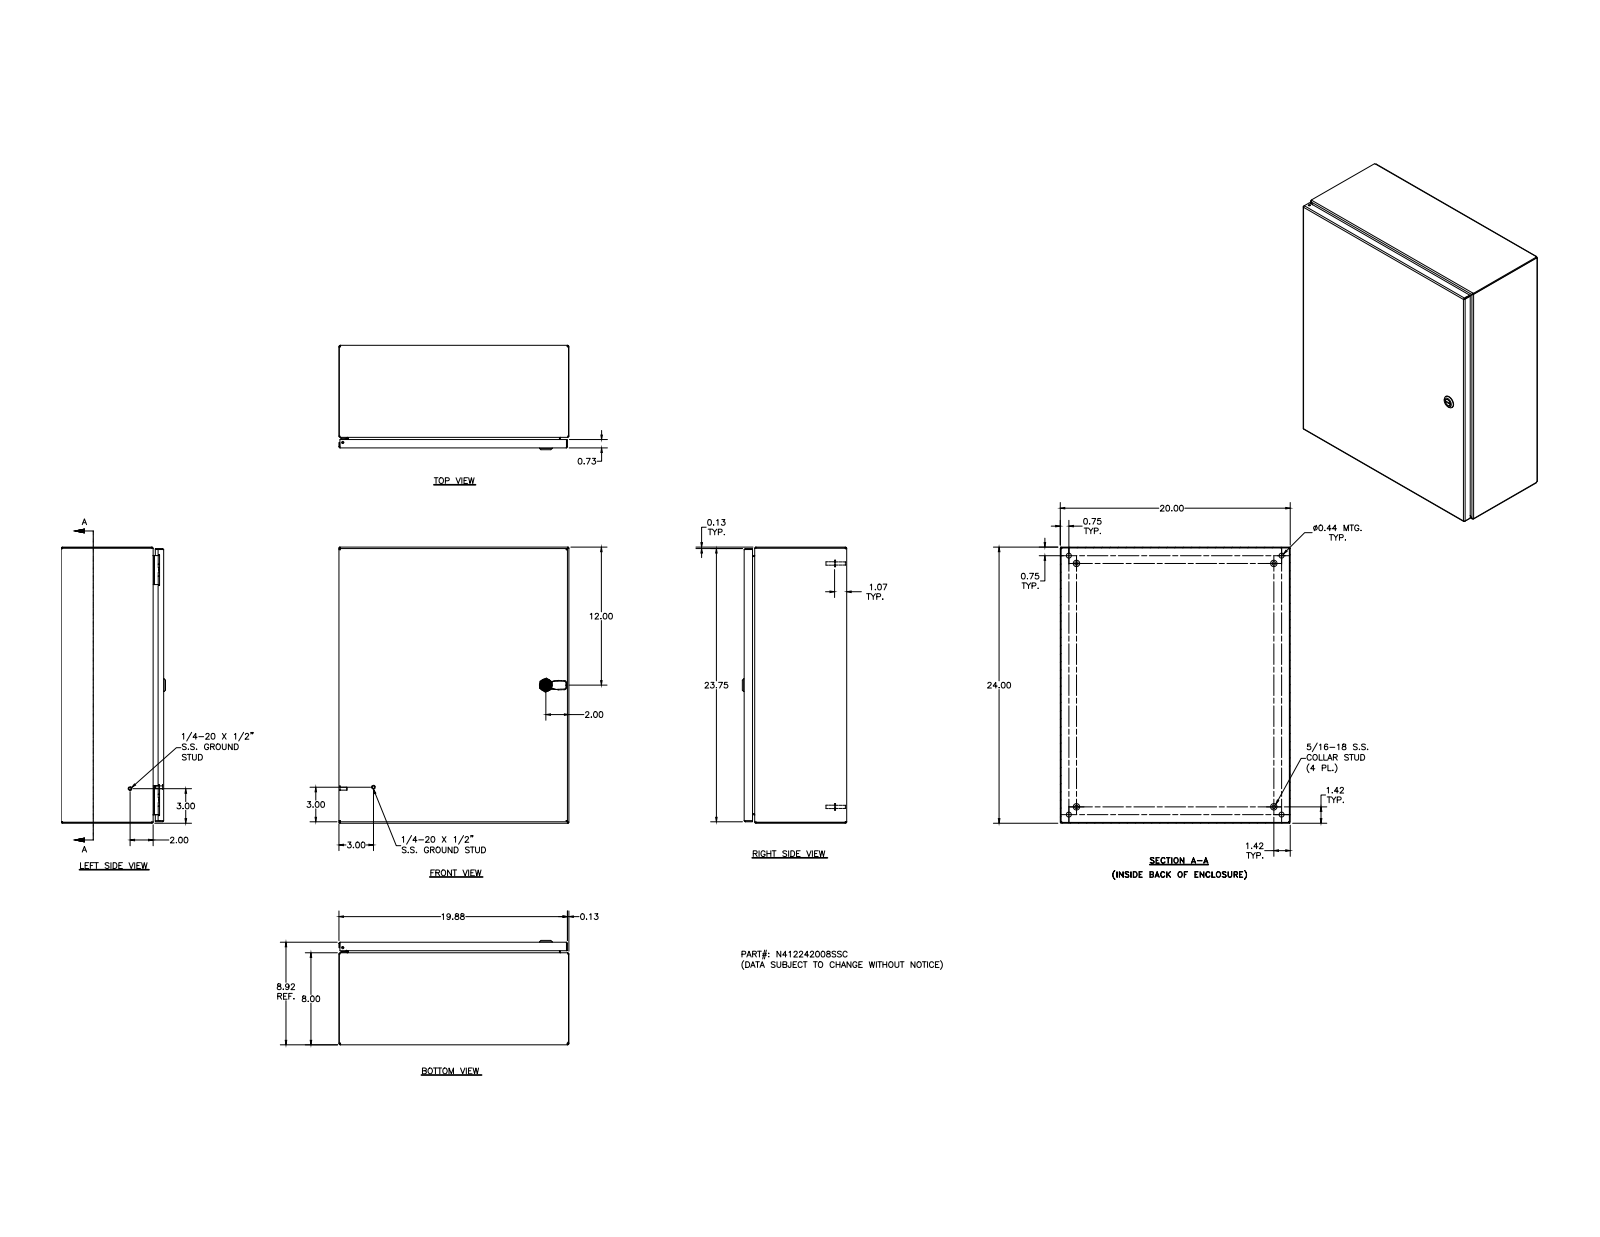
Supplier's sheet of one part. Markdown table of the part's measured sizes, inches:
| quantity | value |
| --- | --- |
| part name | N412242008SSC; N412242008SSCBKP; 388151; N4122420SSCLID (+8 more) |
| STEP written by | Autodesk Inventor 2011 (AUTOMOTIVE_DESIGN) |
| units | inches |
| bodies | 34 solids, 1384 faces (531 planar, 509 cylindrical, 344 other) |
| overall size | 24 × 20 × 9.075 |
| volume | 136.2 in³ |
| surface area | 3 702 in² |
| round holes (diameter × count) | 0.188 × 5, 0.093 × 4, 0.152 × 4, 0.167 × 4, 0.172 × 4, 0.437 × 4, 0.156 × 2, 0.187 × 1, 0.197 × 1, 0.315 × 1, 0.394 × 1, 0.402 × 1 |
| round bosses / shafts (diameter × count) | 0.25 × 10, 0.563 × 4, 0.36 × 4, 0.32 × 4, 0.3 × 4, 0.275 × 4, 0.256 × 4, 0.164 × 4 |
| partial cylindrical surfaces (radius × count) | 0.031 × 30, 0.05 × 26, 0.105 × 20, 0.016 × 18, 0.125 × 14, 0.02 × 9, 0.032 × 8, 0.07 × 8 |
| main face-to-face distances | 0.074, 8.843, 8.769, 8.917, 19.926, 23.926, 20, 19.852, 24, 23.852 |
| hole center spacings | 20, 0.017, 0.66, 18.872, 0.019, 0.5, 0.648, 0.652 |
